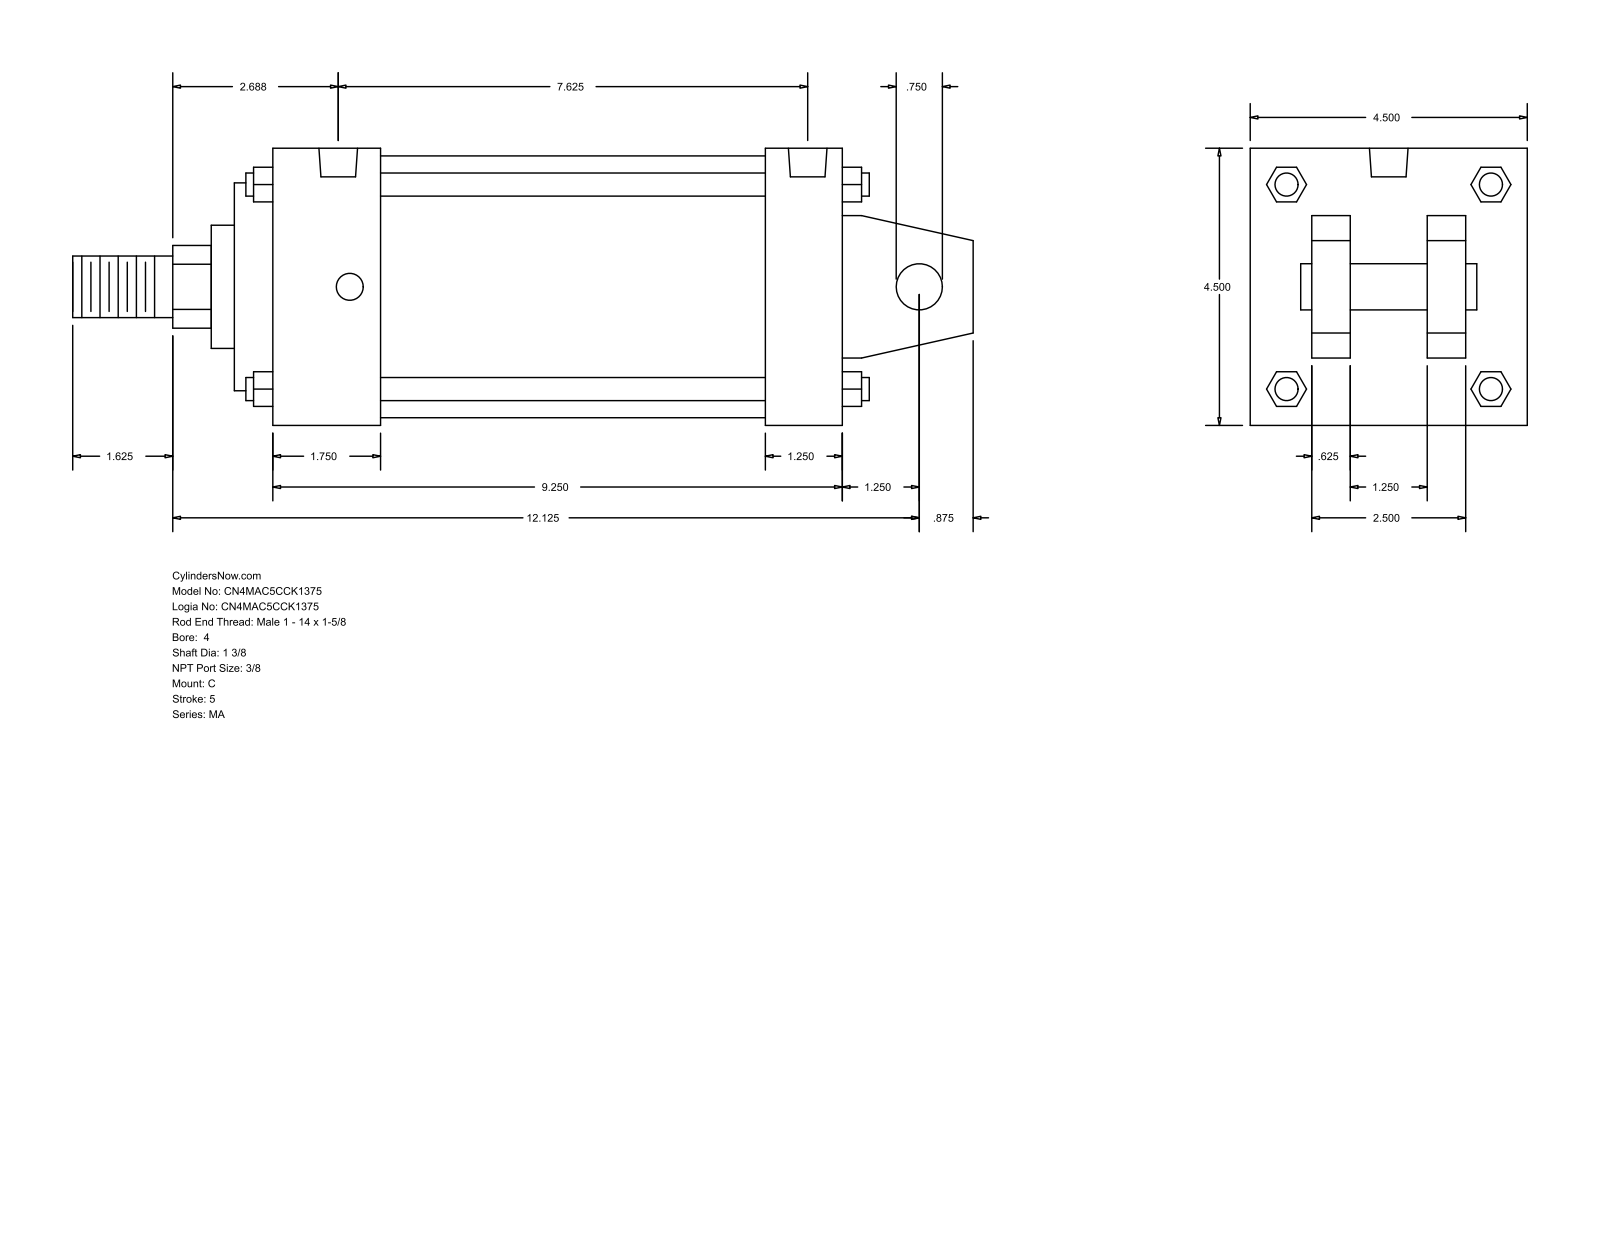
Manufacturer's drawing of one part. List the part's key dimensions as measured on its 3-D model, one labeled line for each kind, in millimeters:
Part name (STEP PRODUCT): MA_C__0400_1.375
STEP written by: GSSL Pune (CONFIG_CONTROL_DESIGN)
Units: millimetres
Bodies: 0 solids, 141 faces (109 planar, 32 cylindrical, 0 other)
Overall size (bounding box): 371.48 × 114.3 × 114.3
Round holes (diameter × count): ⌀11.11 ×4, ⌀15.93 ×2
Round bosses / shafts (diameter × count): ⌀9.53 ×4, ⌀107.95 ×1, ⌀85.72 ×1, ⌀50.8 ×1, ⌀34.92 ×1, ⌀25.4 ×1, ⌀19.05 ×1
Partial cylindrical surfaces — rounded edges, fillets, slot ends (radius × count): R17.06 ×1
Main face-to-face distances: 114.3, 15.87, 234.96, 31.76, 73.03, 41.27, 25.4, 88.9, 47.63, 250.83
Hole centre spacings: 184.15, 4.76, 4.77, 188.91, 188.92, 193.68
